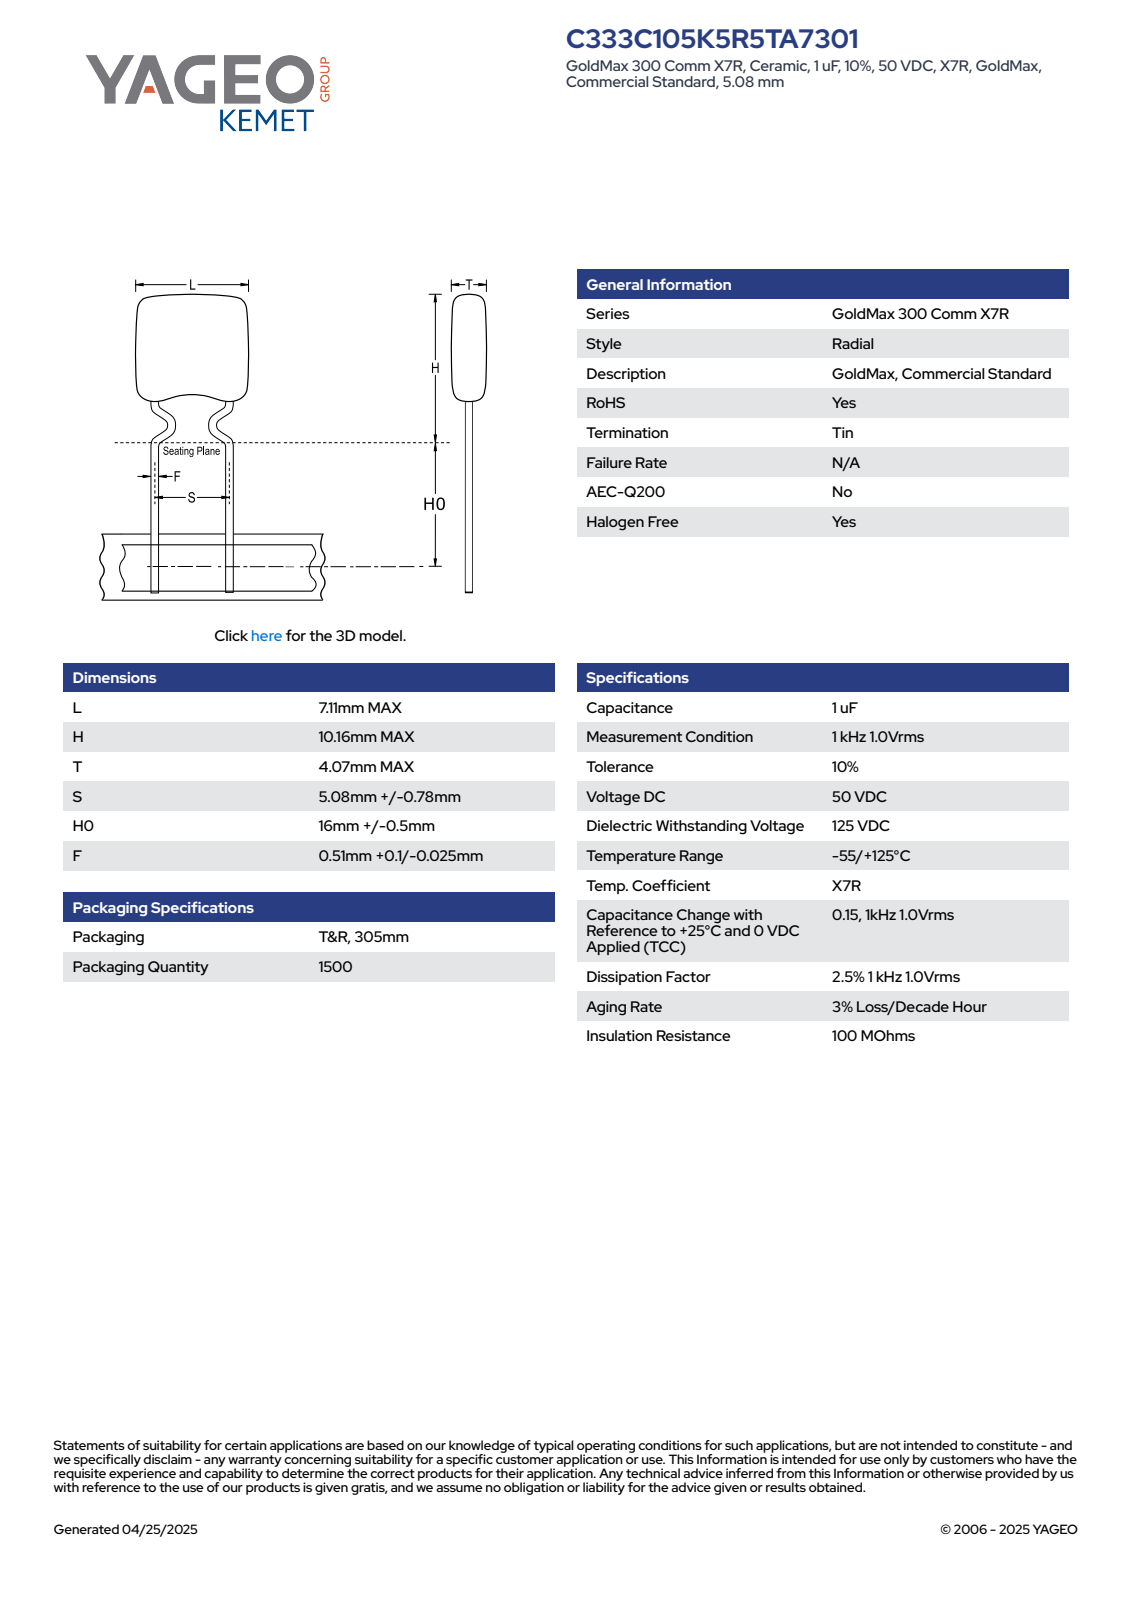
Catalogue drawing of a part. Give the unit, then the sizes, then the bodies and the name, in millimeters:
Units: millimetres
Overall size (bounding box): 26.66 × 7.11 × 4.08
Round bosses / shafts (diameter × count): ⌀0.61 ×2
Partial cylindrical surfaces — rounded edges, fillets, slot ends (radius × count): R1 ×10
Main face-to-face distances: 4.07, 7.11, 6.73, 4.08, 2.88, 3.85, 0.97, 0.42, 1.09, 3.96
Volume: 190 mm³ · Surface area: 266 mm²
Bodies: 4 solids, 102 faces (68 planar, 14 cylindrical, 20 other)
Part name (STEP PRODUCT): CCRC333_L7.11H10.16T4.07S5.86H016.5F0.61
STEP written by: SolidWorks 2014 (AUTOMOTIVE_DESIGN)
